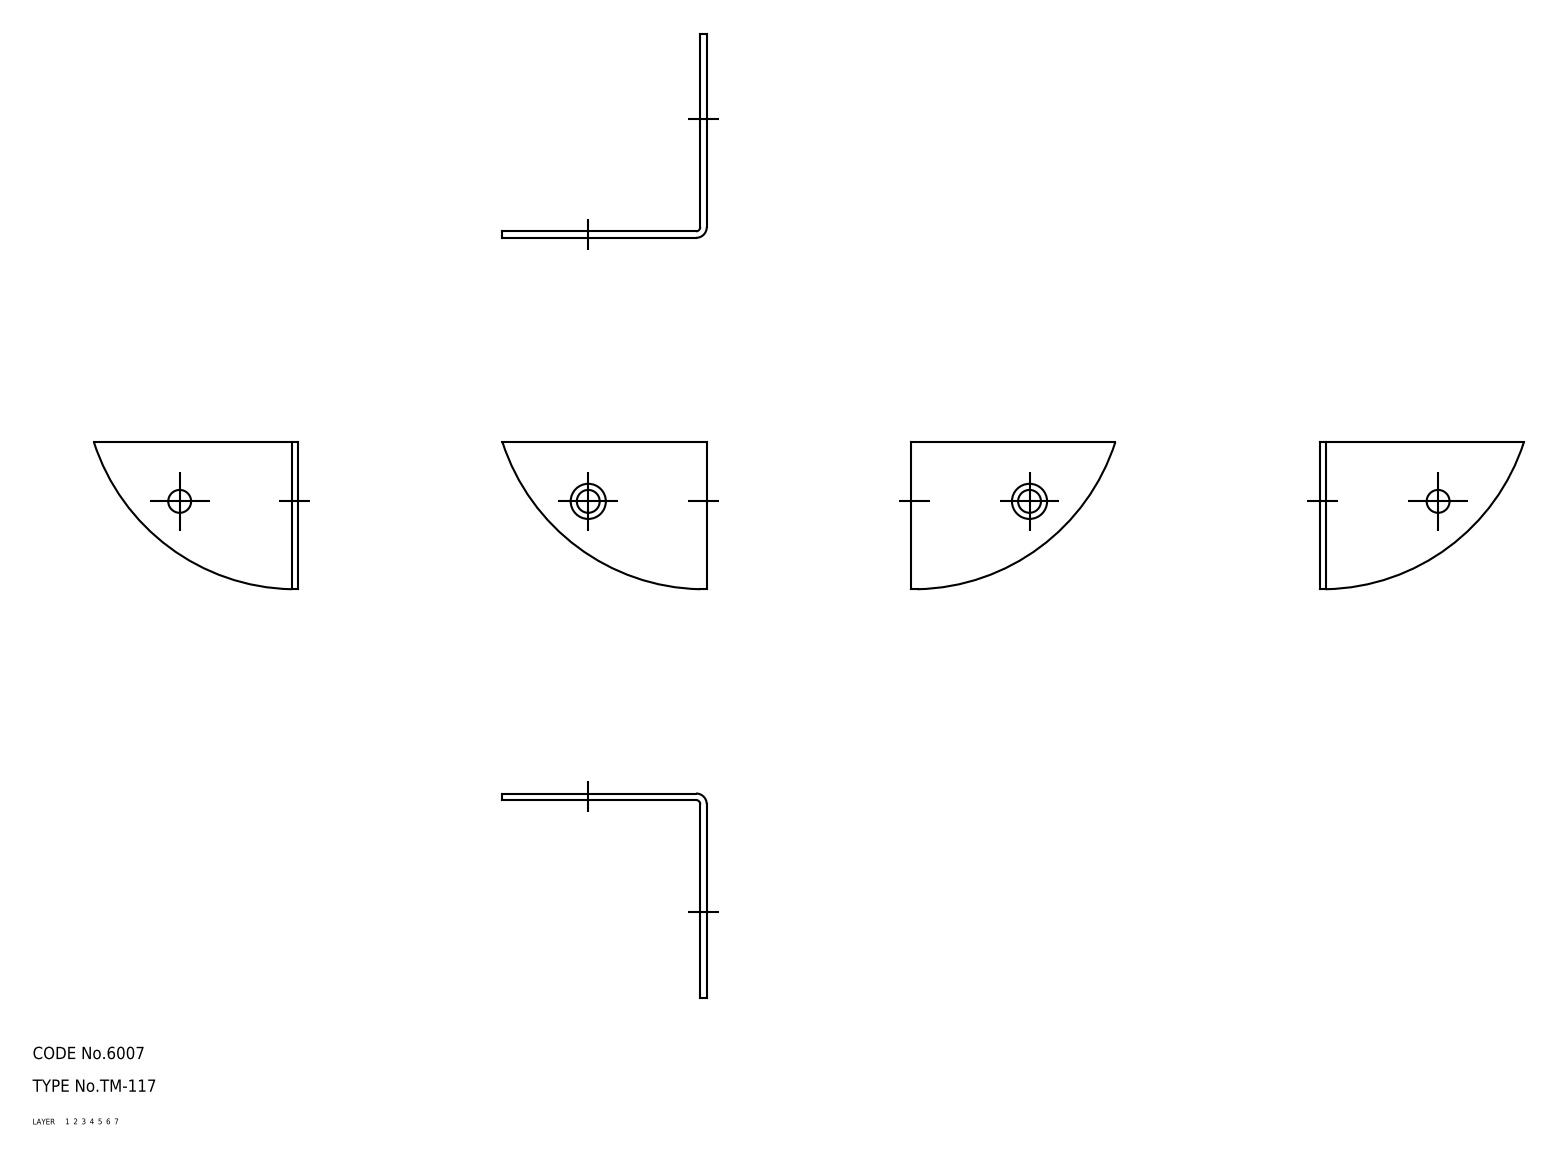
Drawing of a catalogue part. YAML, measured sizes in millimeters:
part_name: "angle"
step_written_by: "CADfix (AUTOMOTIVE_DESIGN)"
units: millimeters
bodies: {solids: 1, faces: 18, planar: 0, cylindrical: 0, other: 18}
overall_size: [50, 50, 36]
volume: 3976
surface_area: 5423
